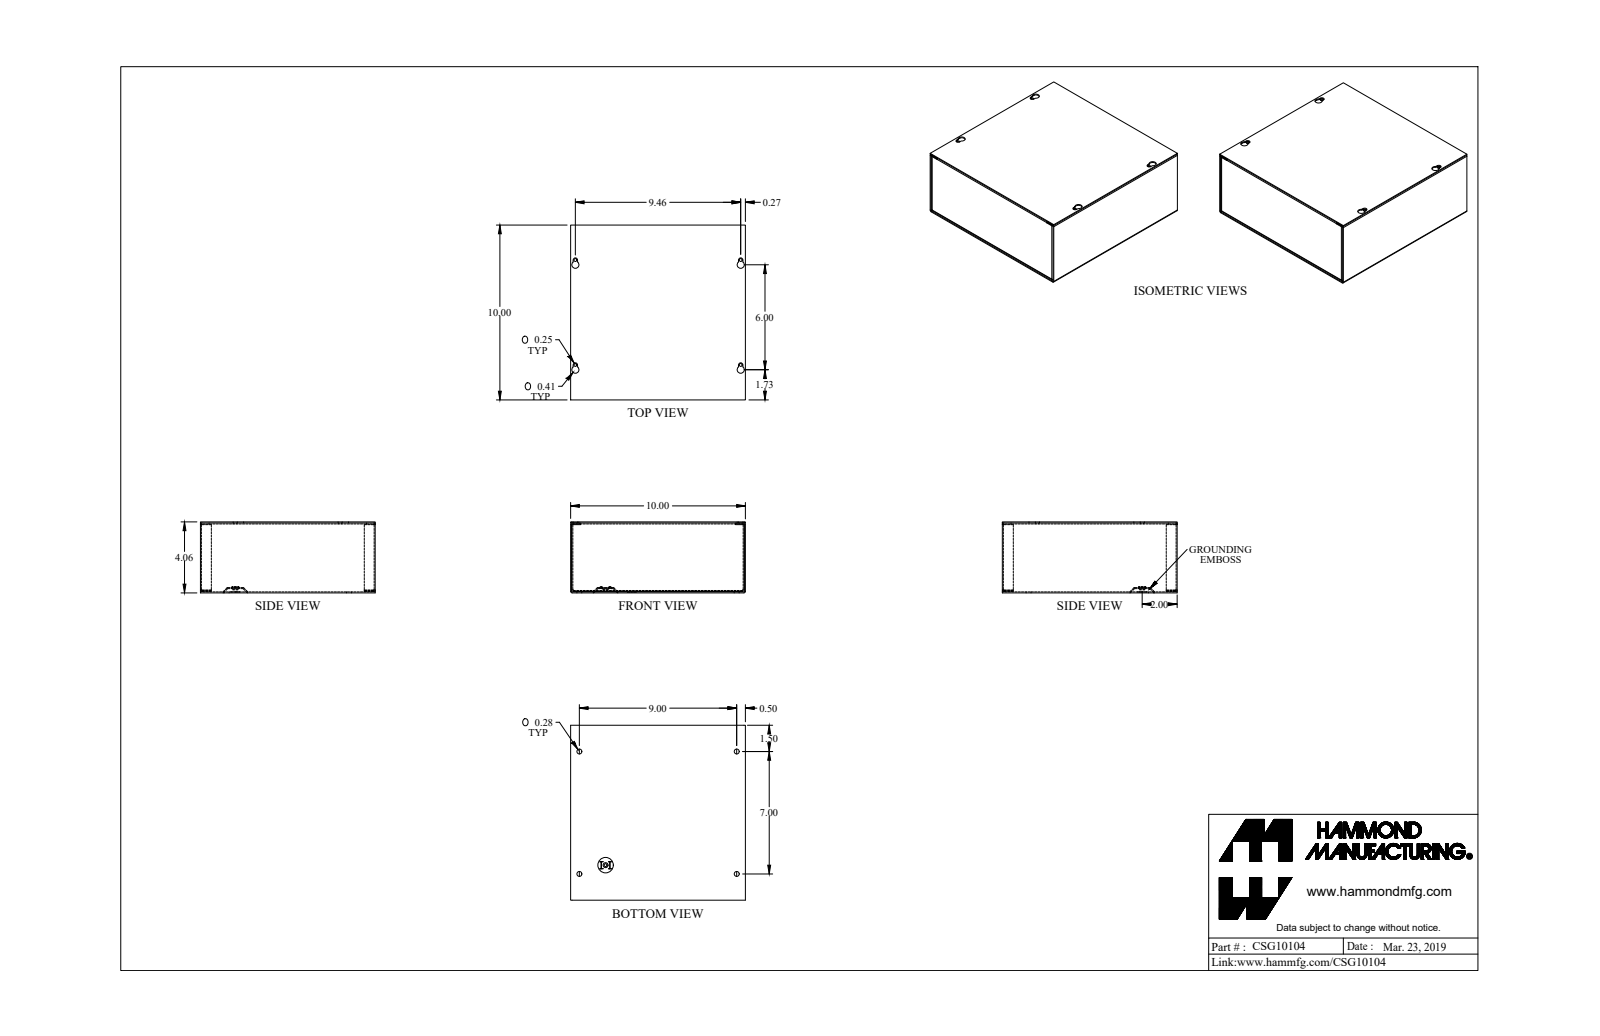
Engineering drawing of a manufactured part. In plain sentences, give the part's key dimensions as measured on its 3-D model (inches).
The part is named "CSG10104_Default". Its 3-D file was written by "SolidWorks 2019 (CONFIG_CONTROL_DESIGN)". It is 4 solids with 205 faces: 125 planar, 72 cylindrical and 8 other. Overall it measures 10 by 10 by 4.057 inches. Its volume is 22.19 cubic inches and its surface area 788.5 square inches. Round holes: 5 of diameter 0.17, 4 of diameter 0.281, 1 of diameter 0.5. Round bosses or shafts: 1 of diameter 0.492, 1 of diameter 0.284. Partial cylindrical surfaces (rounded edges, fillets, slot ends): 12 of radius 0.029, 12 of radius 0.086, 8 of radius 0.057, 4 of radius 0.125, 4 of radius 0.203. The main face-to-face distances are 0.057, 4, 9.943, 3.943, 4.057, 10, 9.886, 0.08, 3.863, 3.92. The hole center spacings are 0.55, 6.504, 9.243, 11.289, 6, 7, 9, 9.46.
